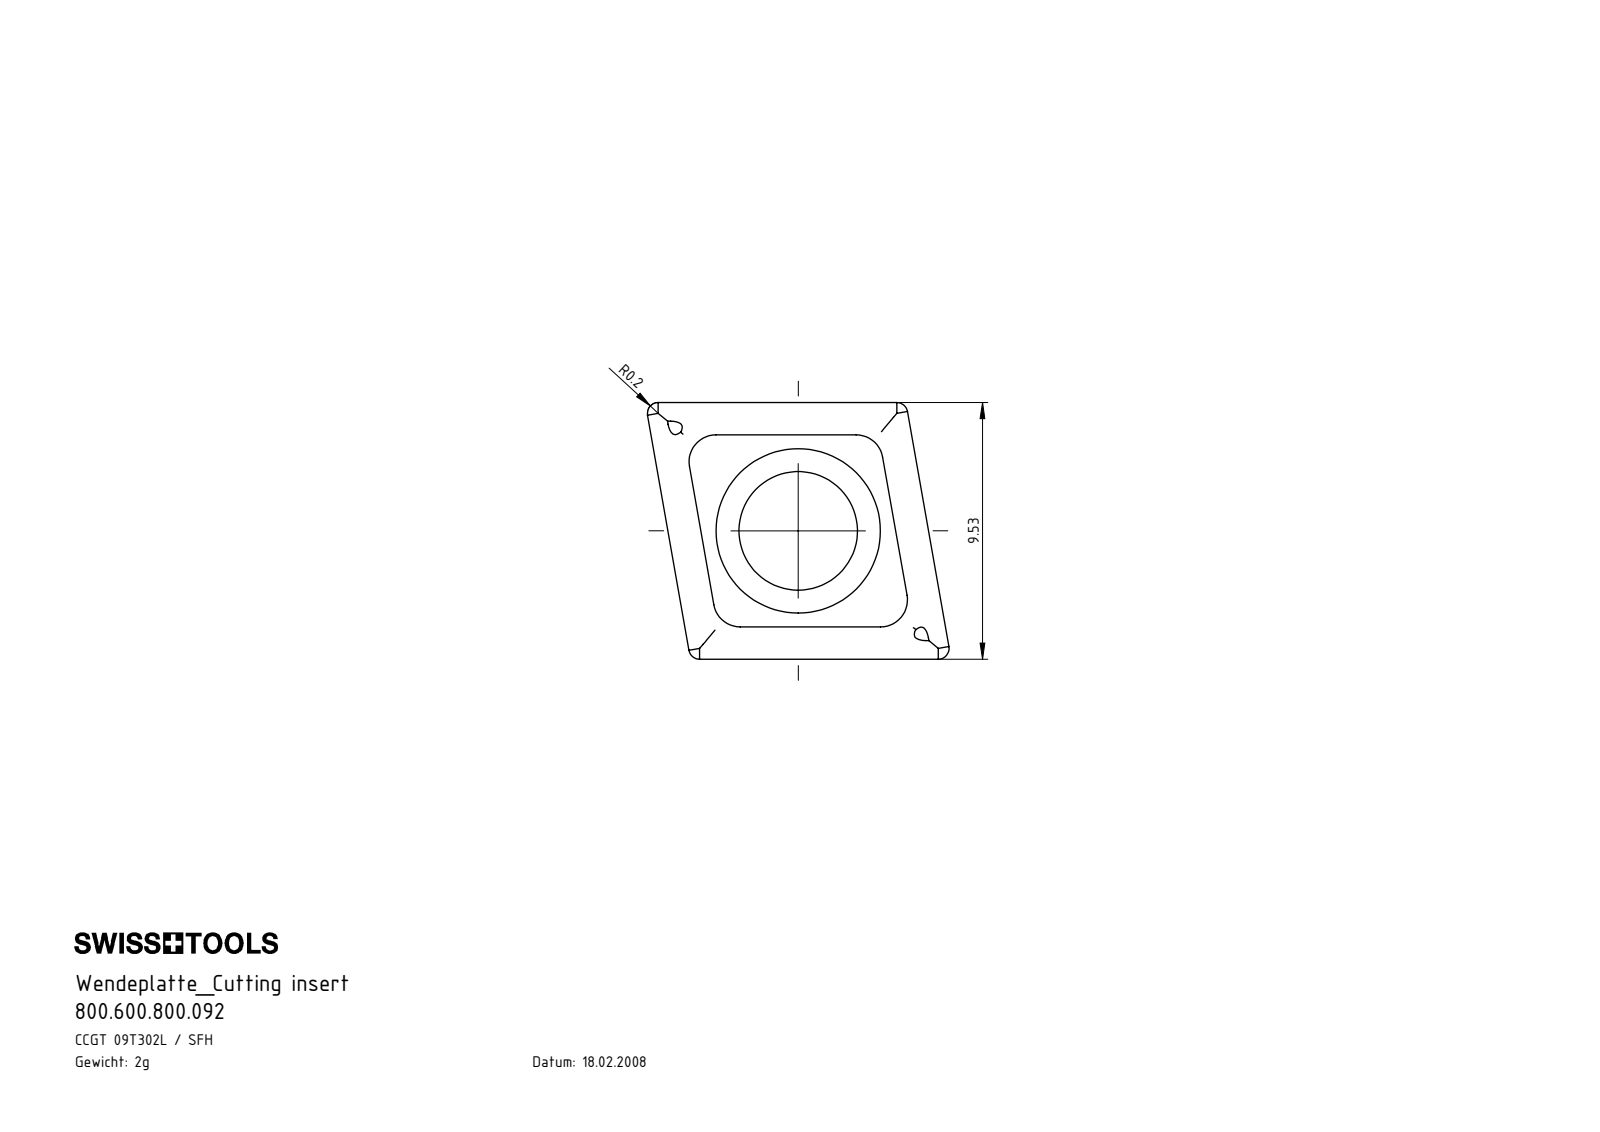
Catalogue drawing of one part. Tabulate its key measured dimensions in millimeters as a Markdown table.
| quantity | value |
| --- | --- |
| part name | CCMT09T304 |
| STEP written by | SolidWorks 2017 (AUTOMOTIVE_DESIGN) |
| units | millimeters |
| bodies | 1 solid, 44 faces (16 planar, 2 cylindrical, 26 other) |
| overall size | 11.2 × 9.53 × 3.97 |
| volume | 240 mm³ |
| surface area | 340 mm² |
| round holes (diameter × count) | 4.4 × 1, 6.1 × 1 |
| main face-to-face distances | 3.97, 4.16, 3.57, 0.4 |
